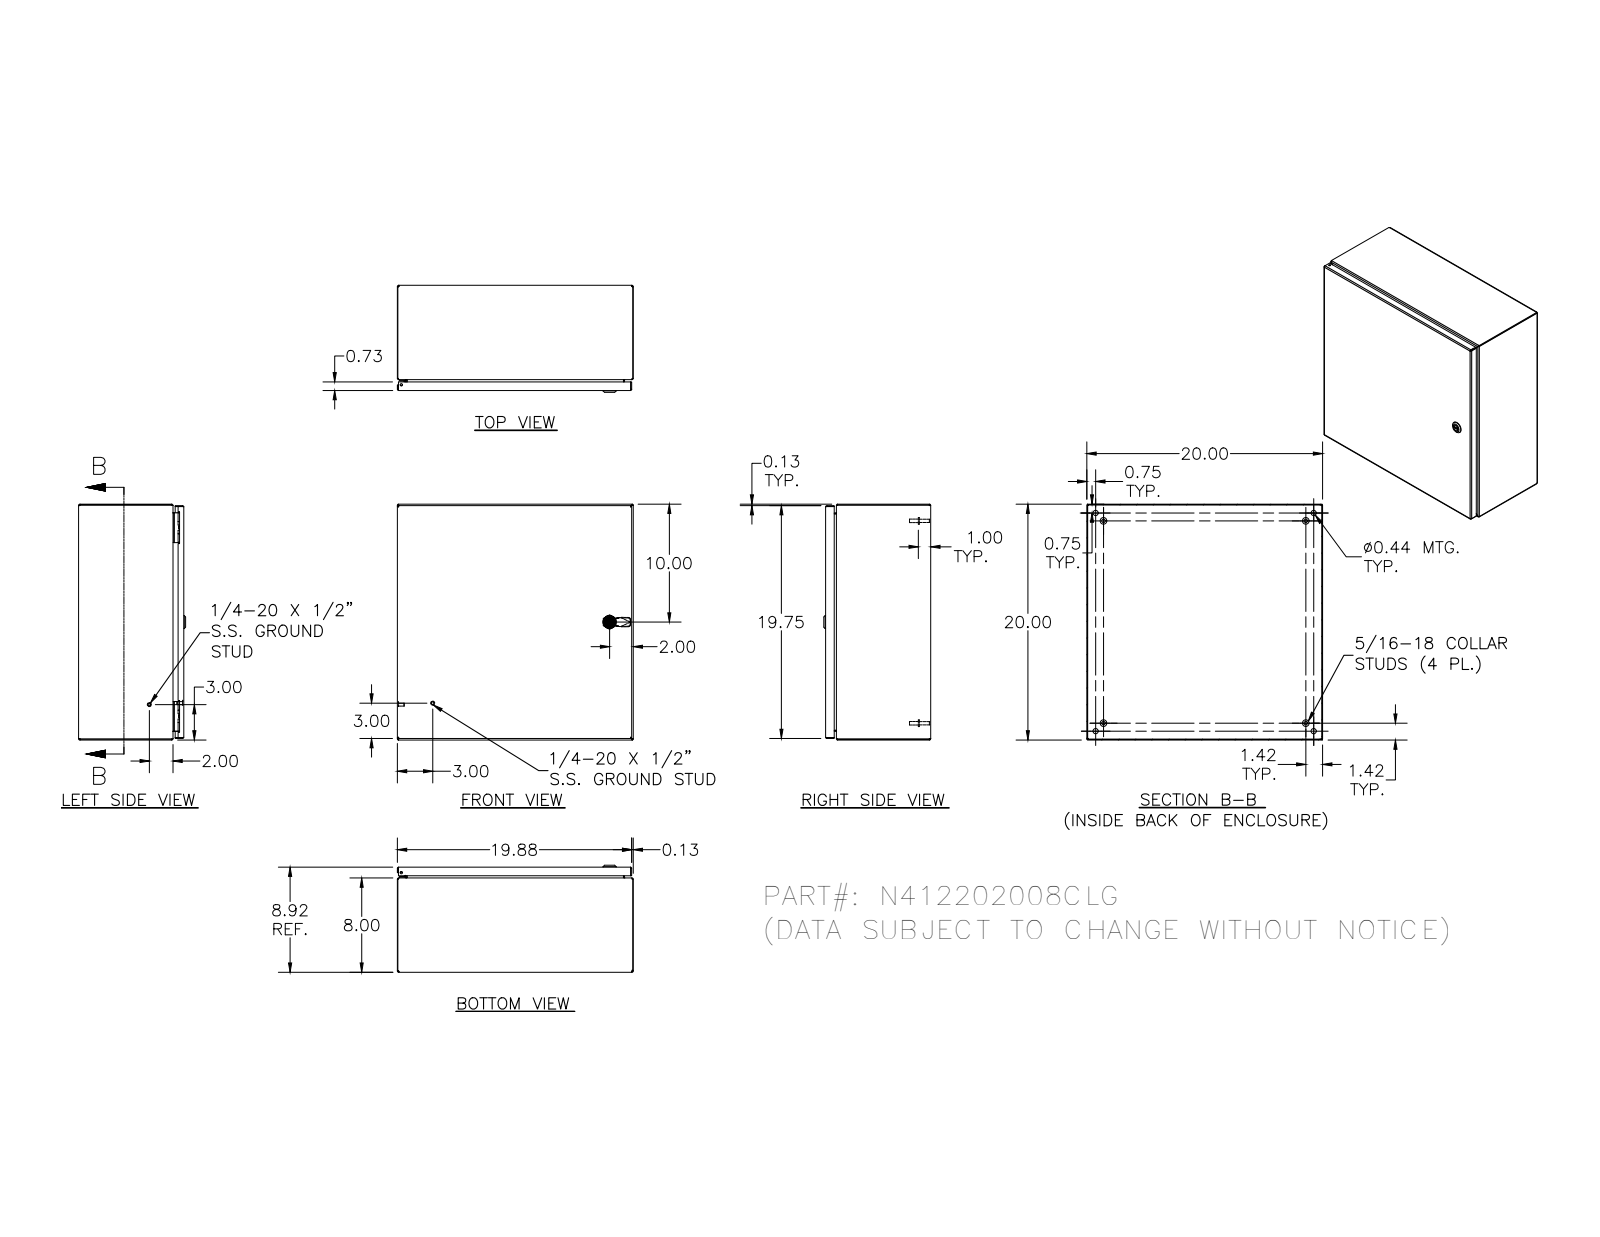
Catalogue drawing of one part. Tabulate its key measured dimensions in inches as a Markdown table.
| quantity | value |
| --- | --- |
| part name | N412202008CLG |
| STEP written by | SolidWorks 2018 (AUTOMOTIVE_DESIGN) |
| units | inches |
| bodies | 33 solids, 1449 faces (530 planar, 547 cylindrical, 372 other) |
| overall size | 20 × 20 × 9.075 |
| volume | 118.6 in³ |
| surface area | 3 225 in² |
| round holes (diameter × count) | 0.188 × 5, 0.093 × 4, 0.152 × 4, 0.167 × 4, 0.172 × 4, 0.437 × 4, 0.156 × 2, 0.187 × 1, 0.197 × 1, 0.315 × 1, 0.394 × 1, 0.402 × 1 |
| round bosses / shafts (diameter × count) | 0.25 × 10, 0.131 × 5, 0.563 × 4, 0.36 × 4, 0.32 × 4, 0.3 × 4, 0.275 × 4, 0.256 × 4 |
| partial cylindrical surfaces (radius × count) | 0.012 × 30, 0.031 × 30, 0.05 × 26, 0.105 × 20, 0.016 × 18, 0.125 × 16, 0.02 × 13, 0.032 × 8 |
| main face-to-face distances | 0.074, 8.843, 8.769, 8.917, 19.926, 19.852, 0.074, 19.926, 20, 0.917 |
| hole center spacings | 16, 0.66, 0.656, 1.307, 1.965, 15.34, 15.996, 16.656 |
